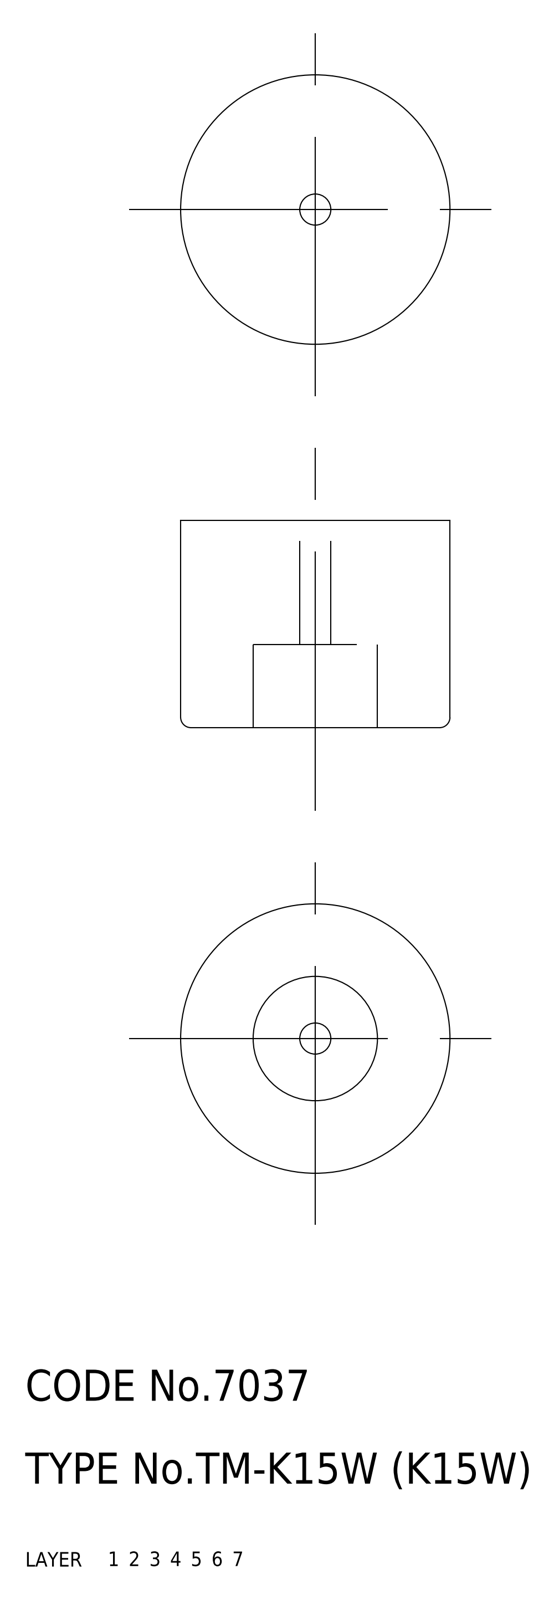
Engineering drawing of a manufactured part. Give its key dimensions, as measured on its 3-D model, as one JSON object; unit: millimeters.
{"part_name": "washer; rubber foot; K15W_6019_36", "step_written_by": "CADfix (AUTOMOTIVE_DESIGN)", "units": "millimeters", "bodies": {"solids": 2, "faces": 23, "planar": 0, "cylindrical": 0, "other": 23}, "overall_size": [26, 26, 20], "volume_mm3": 9633, "surface_area_mm2": 3561}
